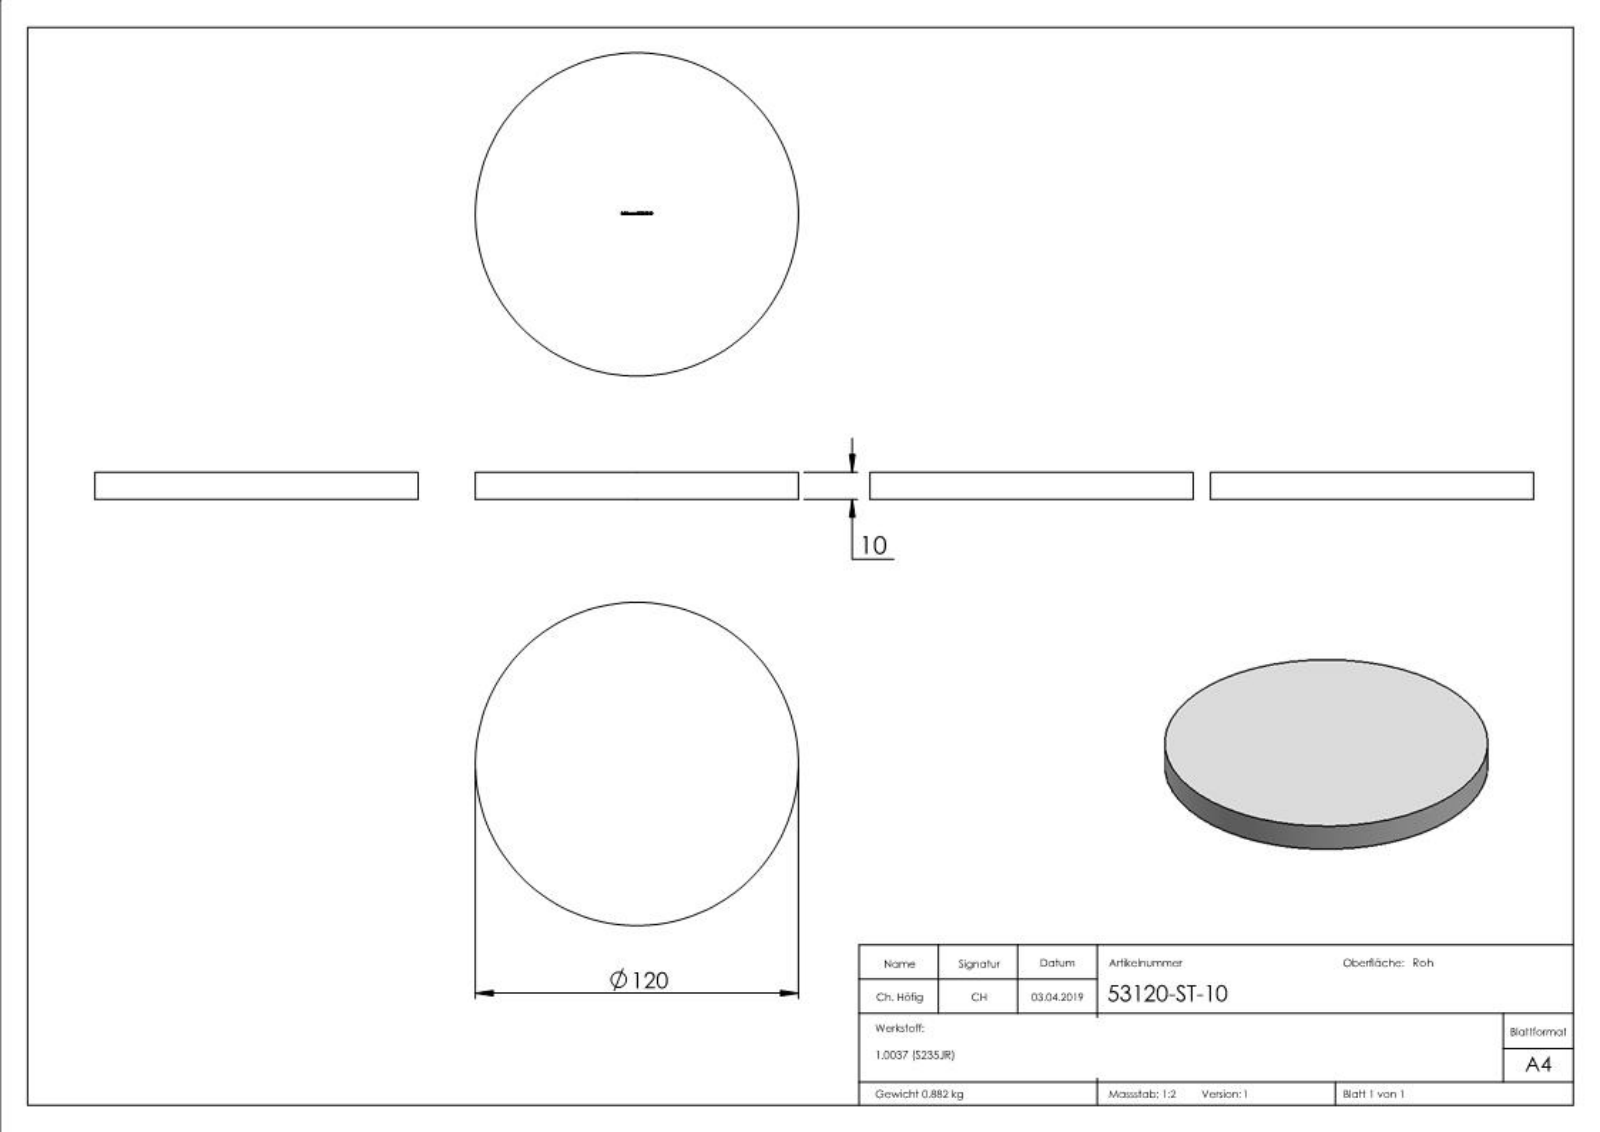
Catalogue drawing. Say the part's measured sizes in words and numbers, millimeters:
The part is named "53120-ST-10". Its 3-D file was written by "SolidWorks 2015 (CONFIG_CONTROL_DESIGN)". It is 1 solid with 236 faces: 125 planar, 2 cylindrical and 109 other. Overall it measures 120 by 120 by 10 millimeters. Its volume is 113 097 cubic millimeters and its surface area 26 395 square millimeters. Round bosses or shafts: 1 of diameter 120. The main face-to-face distances are 10, 9.9, 1.78, 0.98, 0.91, 0.75, 0.44, 0.71, 5.83, 9.39.
